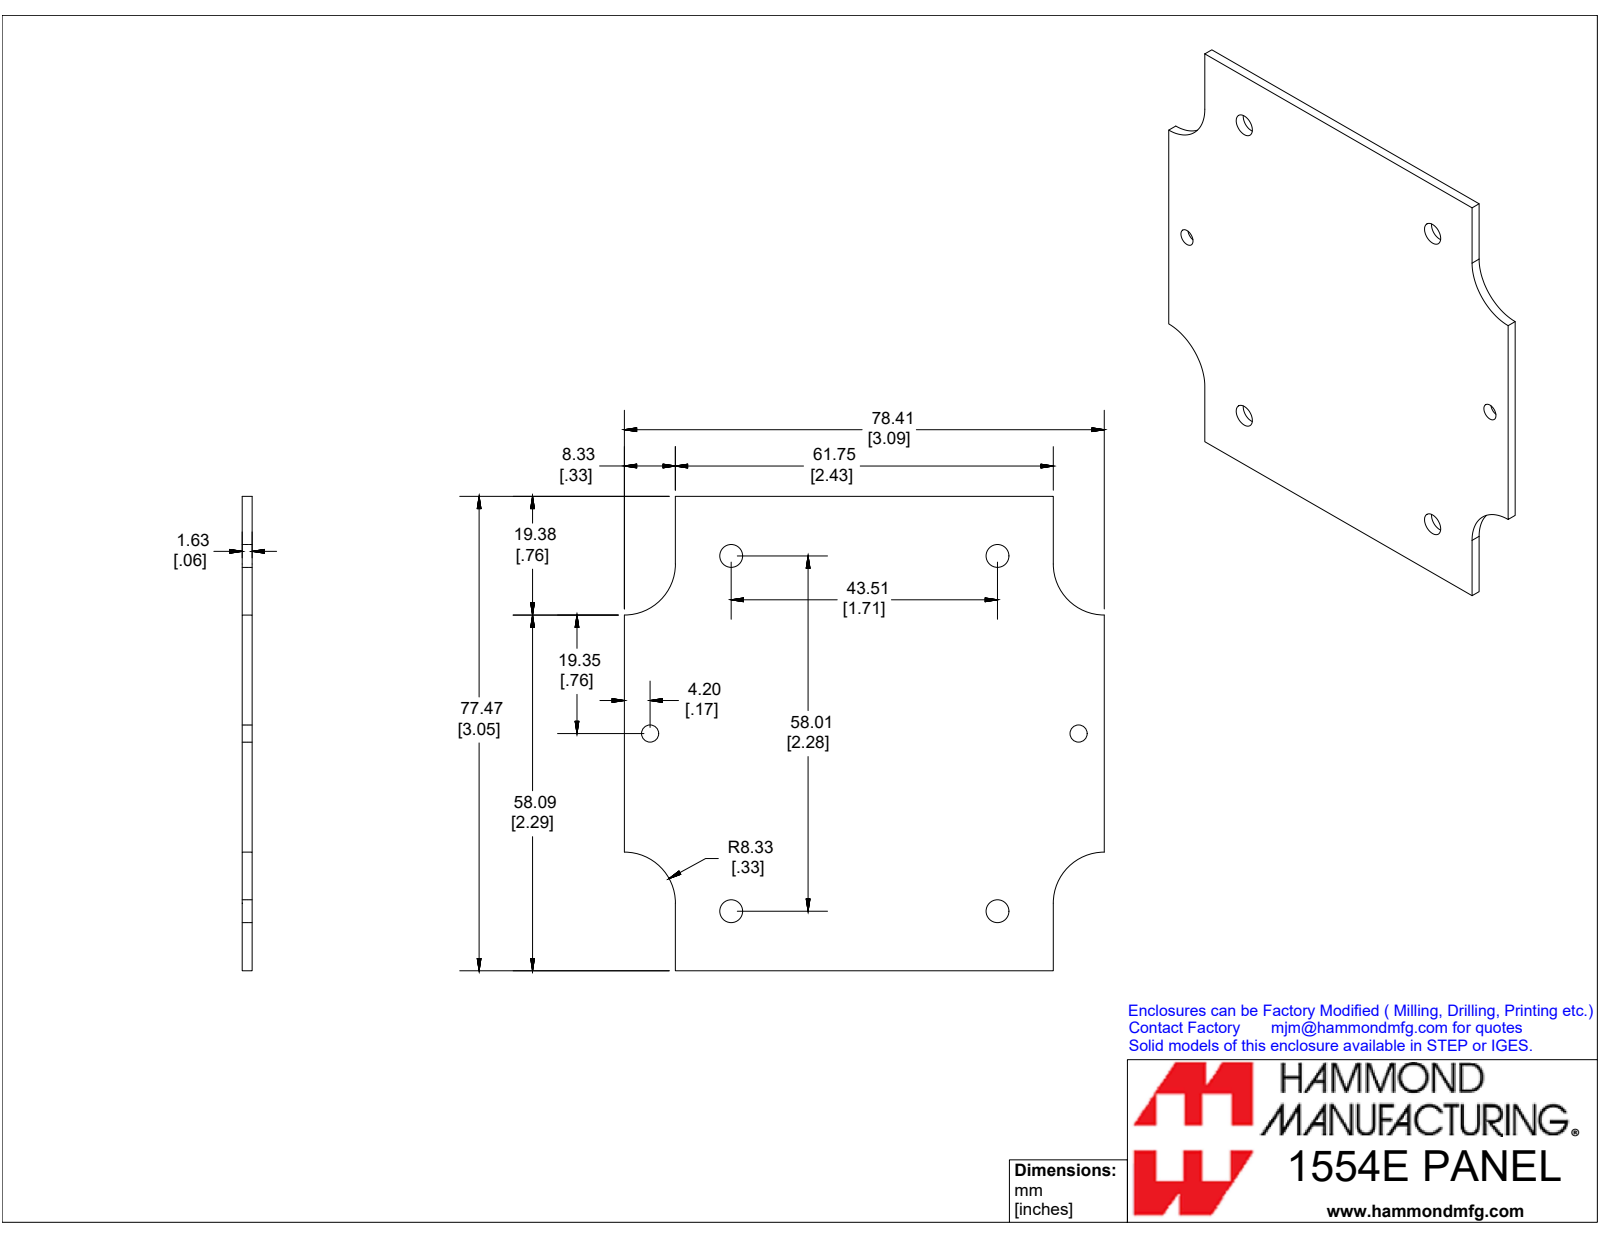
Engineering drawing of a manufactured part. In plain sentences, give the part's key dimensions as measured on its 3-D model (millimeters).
The part is named "1554EPL". Its 3-D file was written by "SolidWorks 2019 (CONFIG_CONTROL_DESIGN)". It is 1 solid with 20 faces: 10 planar, 10 cylindrical and 0 other. Overall it measures 78.4 by 77.5 by 1.6 millimeters. Its volume is 8 830 cubic millimeters and its surface area 11 450 square millimeters. Round holes: 4 of diameter 3.7, 2 of diameter 2.8. Partial cylindrical surfaces (rounded edges, fillets, slot ends): 4 of radius 8.3. The main face-to-face distances are 1.6, 77.5, 8.3, 70.1, 78.4, 61.7. The hole center spacings are 31.9, 63.7, 43.5, 58, 72.5, 70.
